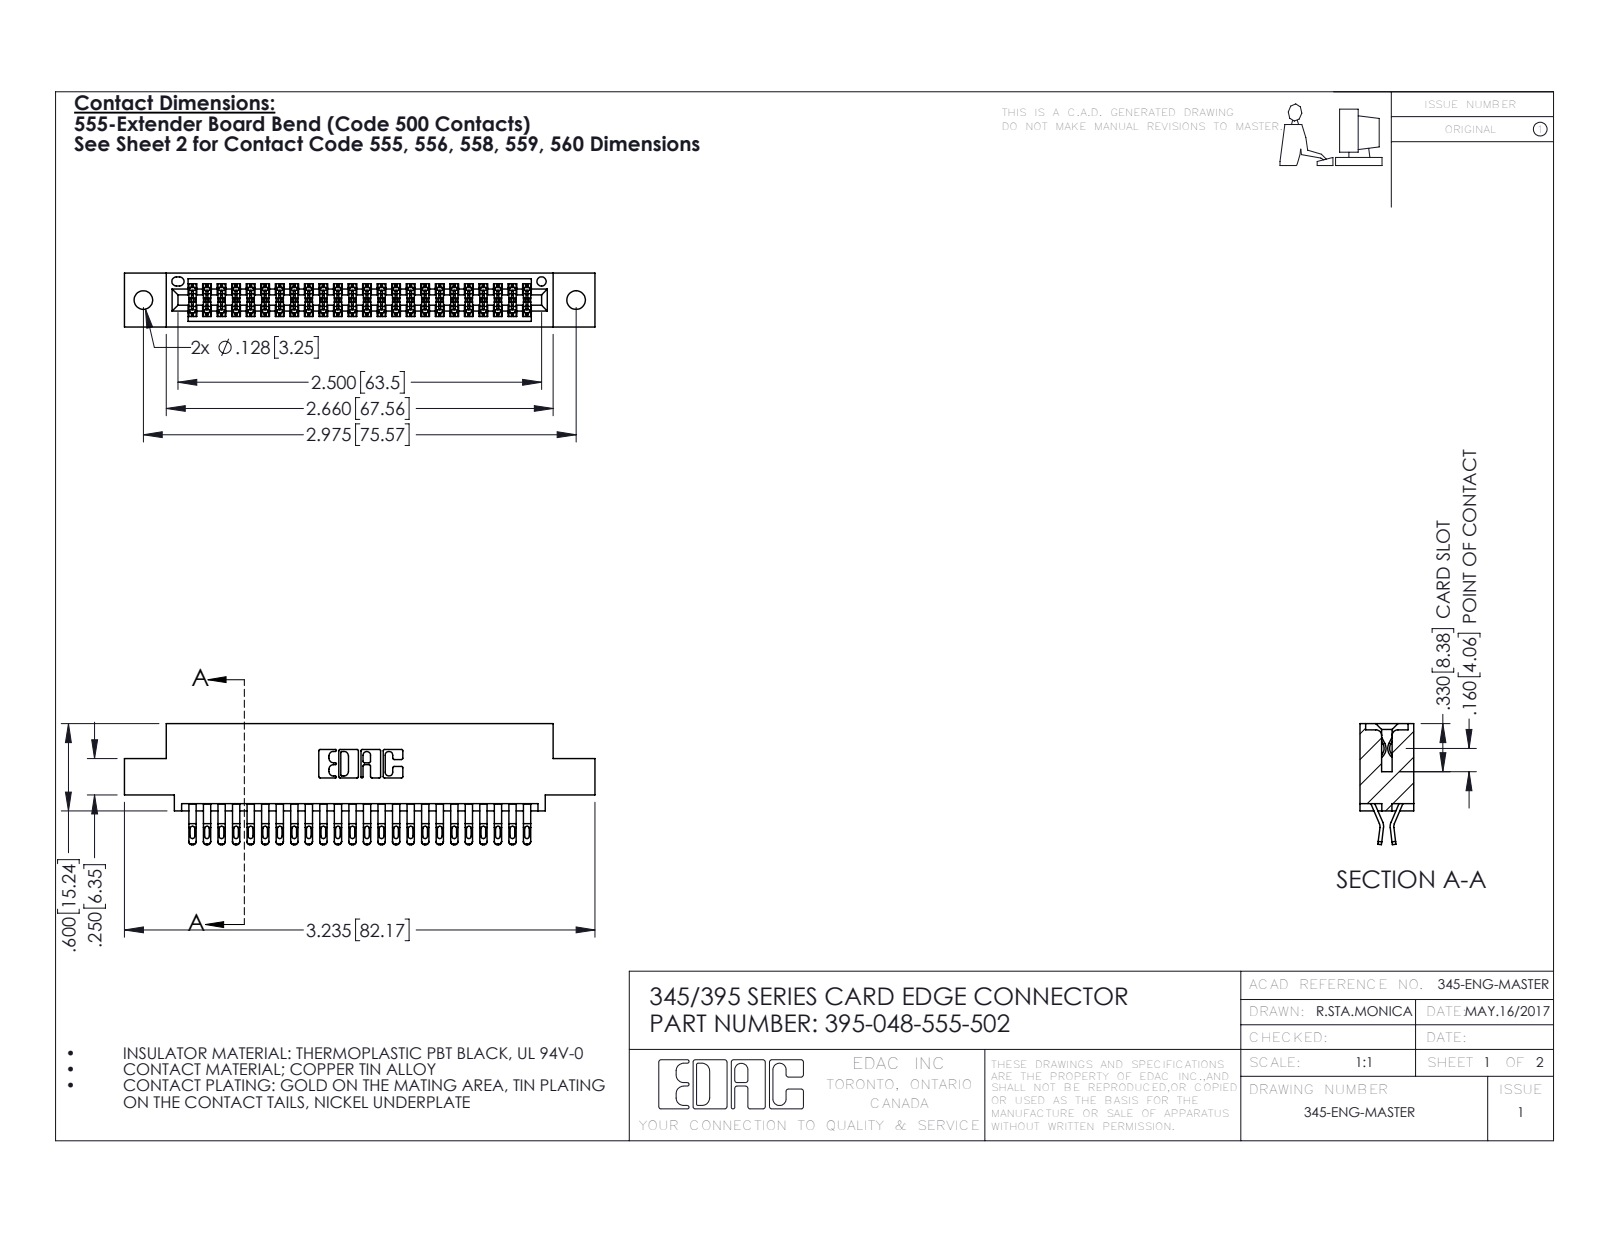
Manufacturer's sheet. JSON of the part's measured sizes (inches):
{"part_name": "345 Part_0.110 Offset - 0.128 Dia; 345-292-001_555 Tail; 395-048-555-502", "step_written_by": "SolidWorks 2016 (CONFIG_CONTROL_DESIGN)", "units": "inches", "bodies": {"solids": 49, "faces": 2818, "planar": 1572, "cylindrical": 1246, "other": 0}, "overall_size": [3.235, 0.832, 0.37], "volume_in3": 0.479, "surface_area_in2": 17.9, "round_holes": [[0.128, 2], [0.064, 1]], "partial_cylinders_radius": [[0.016, 120], [0.02, 96], [0.006, 72], [0.01, 22], [0.007, 6], [0.031, 6], [0.026, 3], [0.01, 2]], "face_to_face_distances": [0.298, 0.072, 0.37, 0.2, 0.025, 0.098, 0.272, 0.225, 0.175, 0.149], "hole_center_spacings": [0.27, 2.741, 2.975]}
